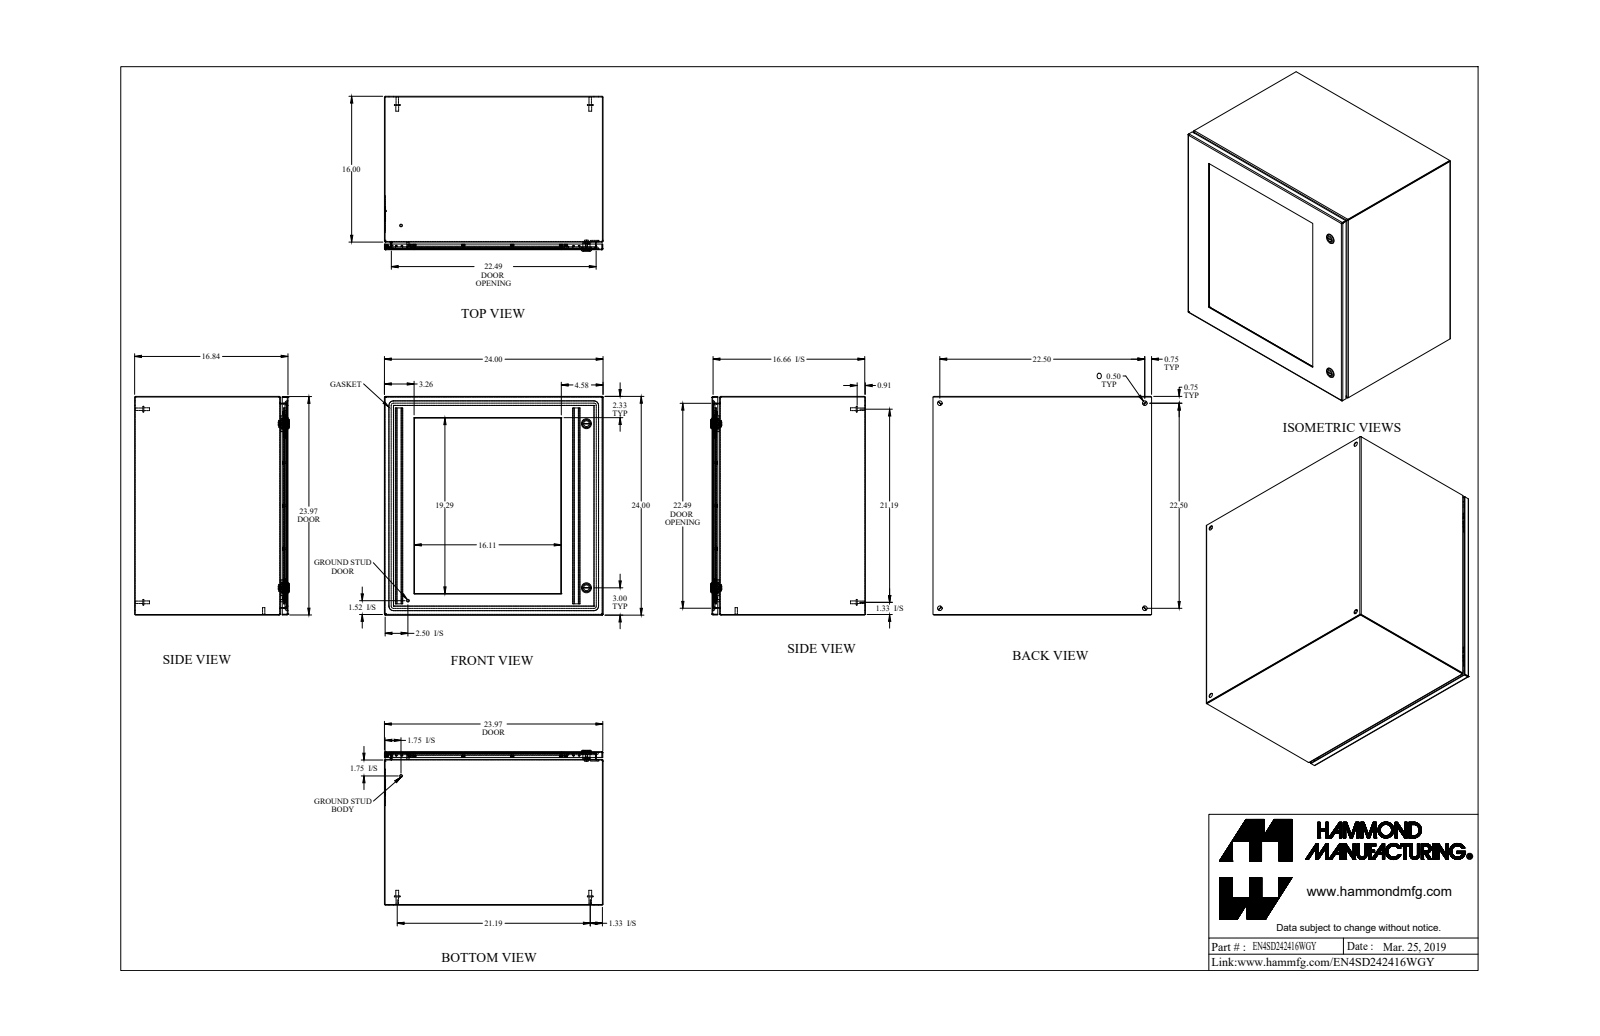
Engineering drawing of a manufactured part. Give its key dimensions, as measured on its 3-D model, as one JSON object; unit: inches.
{"part_name": "EN4SD242416WGY", "step_written_by": "SolidWorks 2019 (AUTOMOTIVE_DESIGN)", "units": "inches", "bodies": {"solids": 74, "faces": 1435, "planar": 740, "cylindrical": 441, "other": 254}, "overall_size": [24, 24, 16.997], "volume_in3": 285.6, "surface_area_in2": 6420, "round_holes": [[0.13, 18], [0.25, 18], [0.5, 4], [0.232, 2], [0.625, 2], [0.785, 2], [0.172, 1], [0.24, 1], [0.242, 1]], "round_bosses_or_shafts": [[0.226, 19], [0.368, 18], [0.164, 18], [0.625, 4], [0.313, 4], [0.27, 4], [1.1, 2], [0.525, 2]], "partial_cylinders_radius": [[0.036, 14], [0.108, 14], [0.043, 12], [0.081, 12], [0.125, 12], [0.312, 12], [0.1, 8], [0.006, 4]], "face_to_face_distances": [0.072, 23.928, 16.765, 23.856, 24, 16.693, 16.443, 0.25, 16.515, 0.322], "hole_center_spacings": [5.372, 17.781, 4.719, 19.57, 21.03, 5.372, 9.437, 10.743]}
